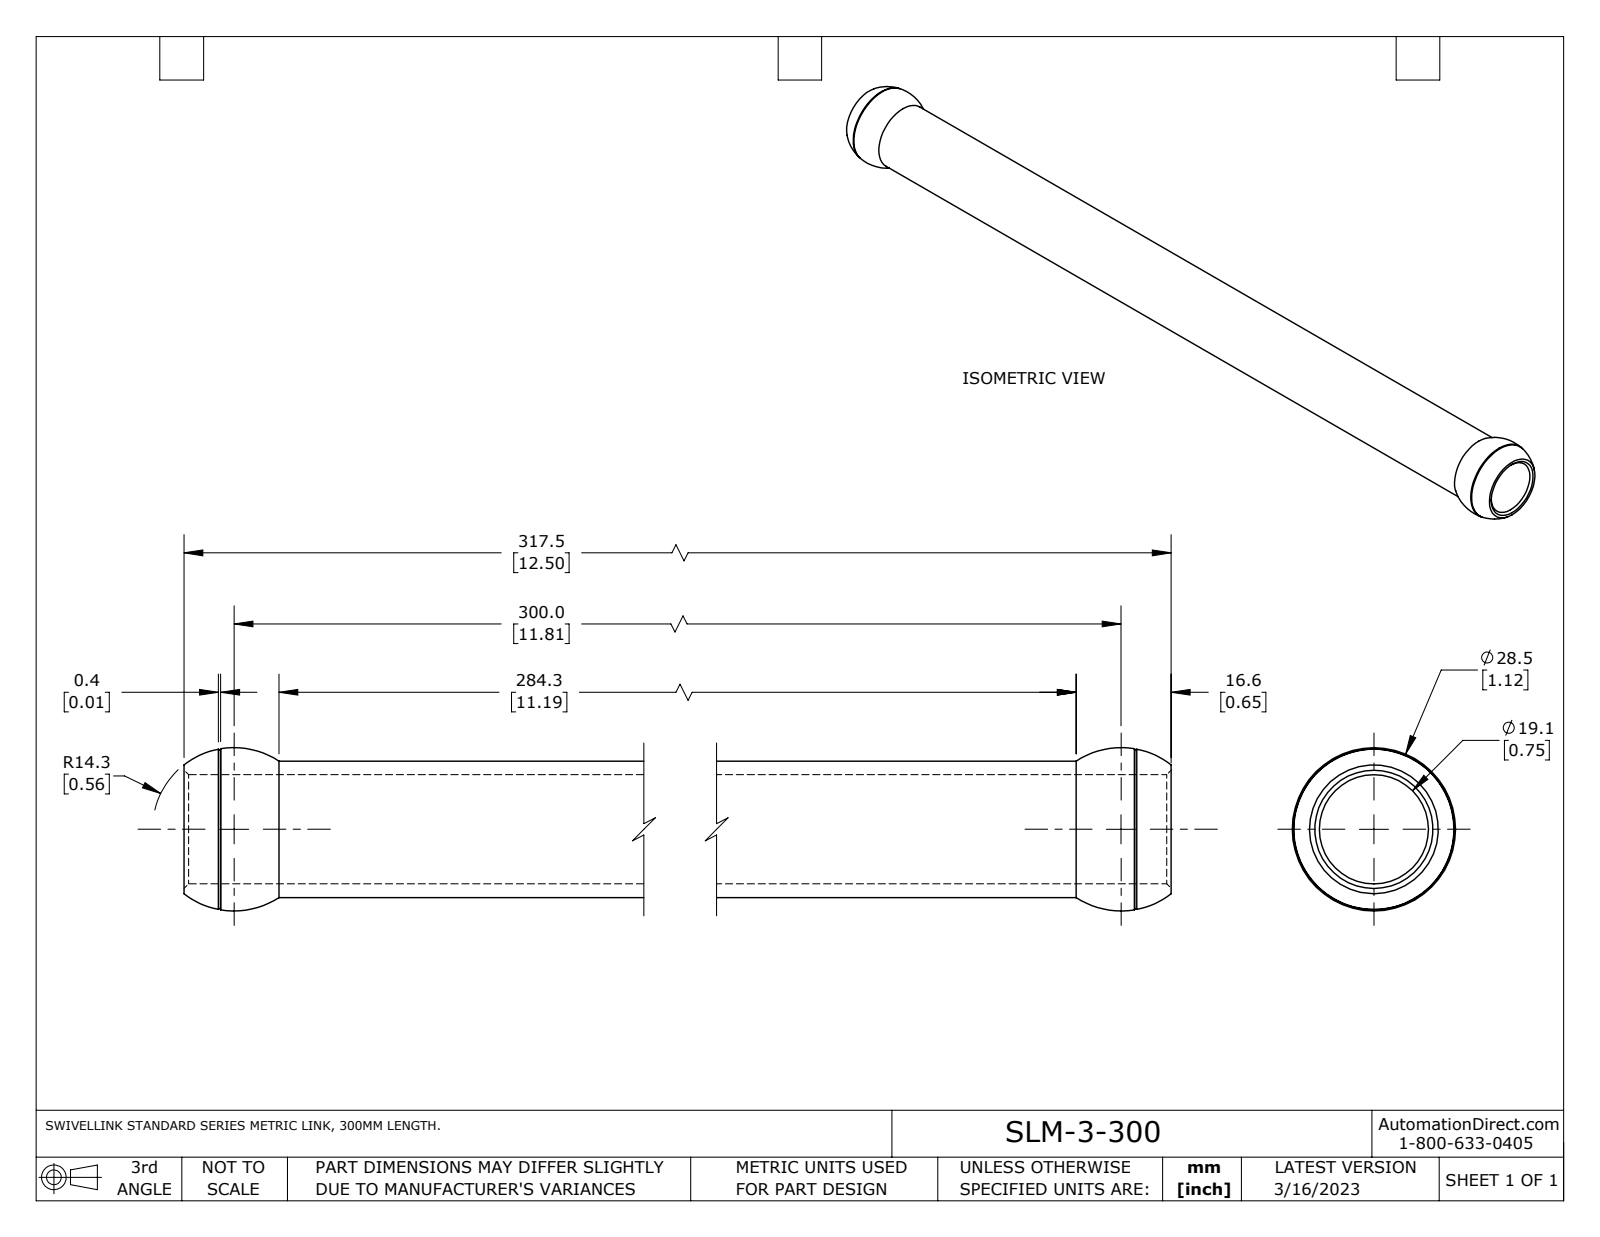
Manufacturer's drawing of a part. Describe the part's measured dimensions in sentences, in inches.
The part is named "SLM-3-300". Its 3-D file was written by "SolidWorks 2021 (AUTOMOTIVE_DESIGN)". It is 2 solids with 14 faces: 2 planar, 2 cylindrical and 10 other. Overall it measures 12.933 by 1.107 by 1.107 inches. Its volume is 13.2 cubic inches and its surface area 69.6 square inches. Round bosses or shafts: 1 of diameter 0.937, 1 of diameter 0.75. The main face-to-face distances are 12.5.
